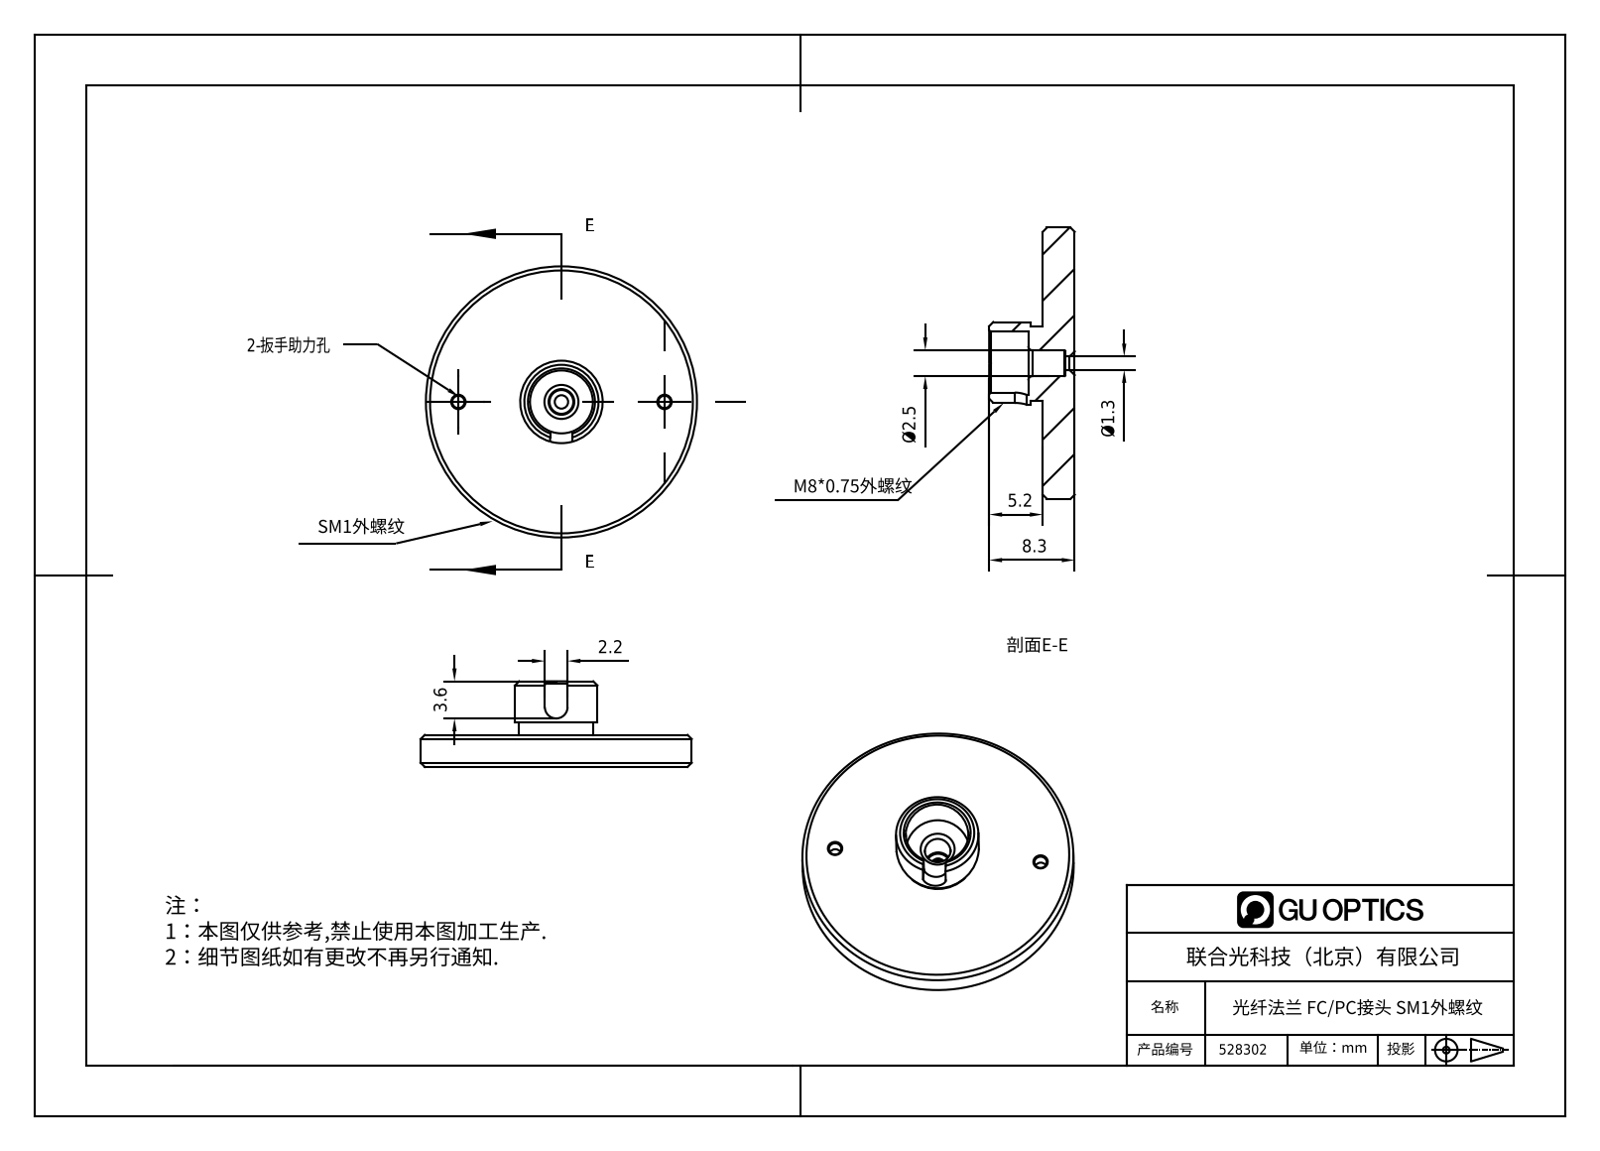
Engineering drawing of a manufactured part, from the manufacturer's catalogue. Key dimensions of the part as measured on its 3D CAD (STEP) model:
Part name (STEP PRODUCT): 528302，光纤法兰 FC-PC接头 SM1外螺纹
STEP written by: SolidWorks 2020 (CONFIG_CONTROL_DESIGN)
Units: millimetres
Bodies: 1 solid, 46 faces (10 planar, 17 cylindrical, 19 other)
Overall size (bounding box): 26.3 × 26.3 × 8.3
Volume: 1 778 mm³ · Surface area: 1 545 mm²
Round holes (diameter × count): ⌀1.2 ×2, ⌀1.3 ×1, ⌀2.5 ×1, ⌀6.1 ×1
Round bosses / shafts (diameter × count): ⌀26.3 ×1, ⌀8 ×1, ⌀7.2 ×1
Partial cylindrical surfaces — rounded edges, fillets, slot ends (radius × count): R1.1 ×1
Main face-to-face distances: 3.1, 4.5, 1.4, 4.3, 1.2, 8.3, 5.2, 4, 3.8, 2.2
Hole centre spacings: 10, 20
